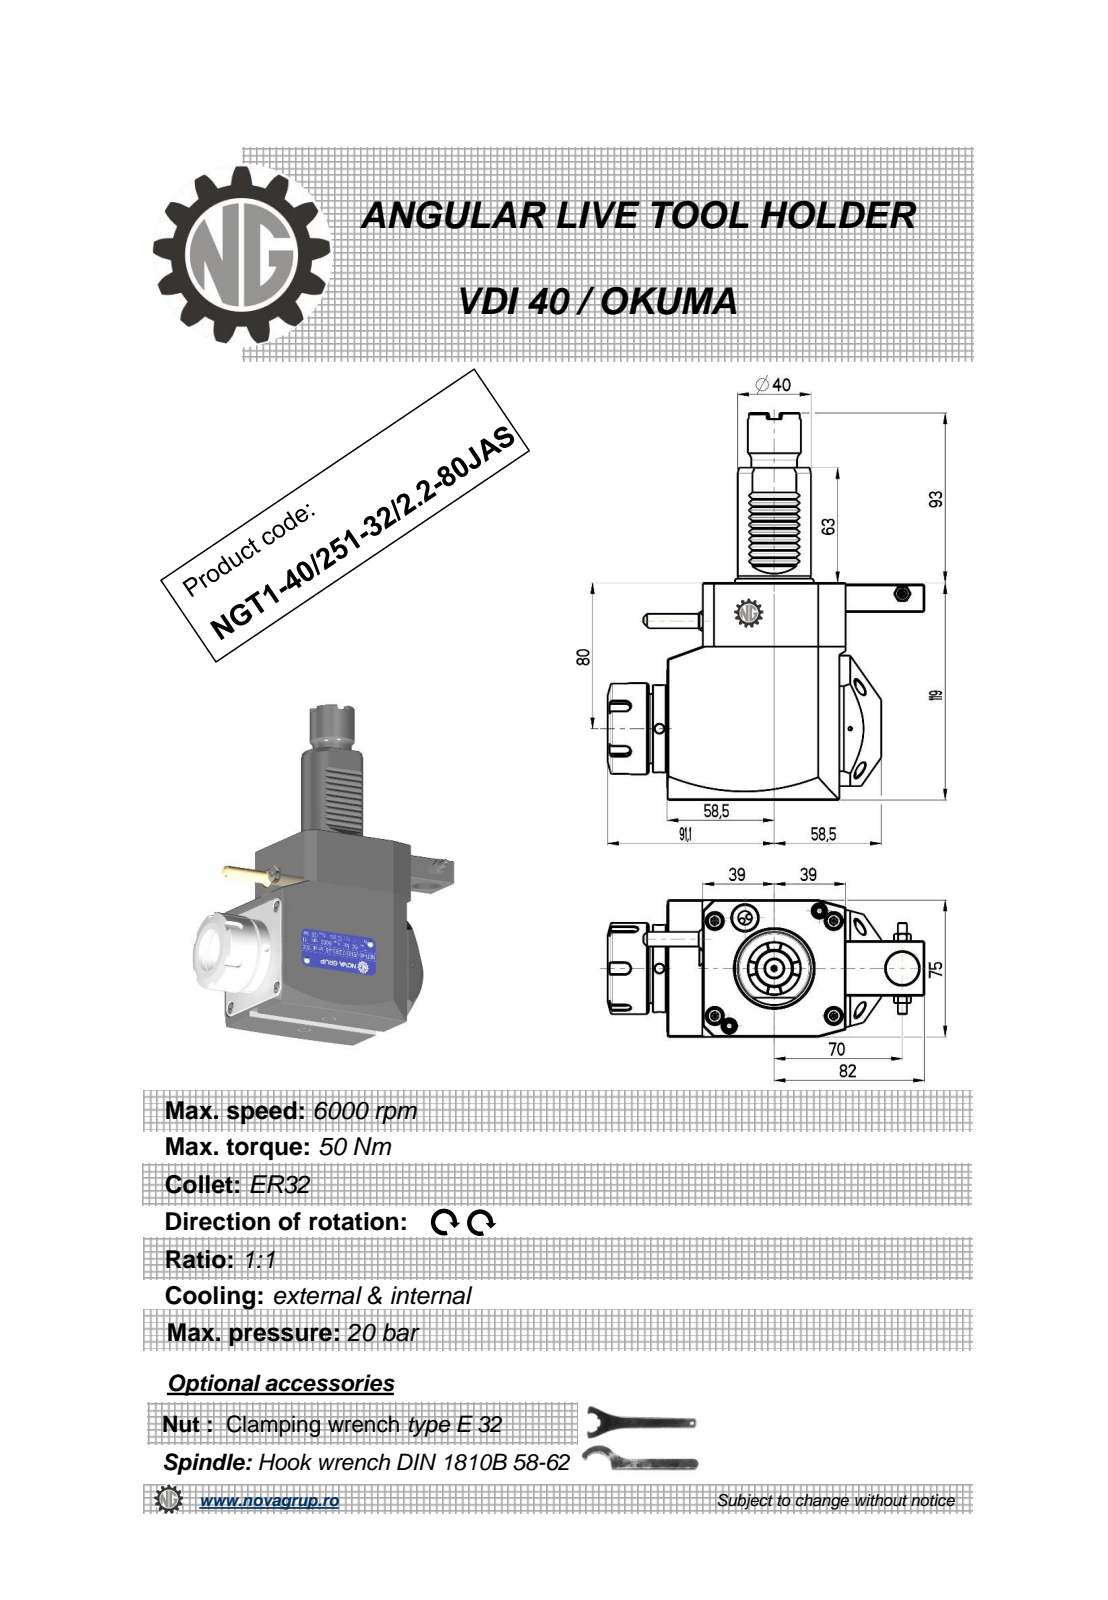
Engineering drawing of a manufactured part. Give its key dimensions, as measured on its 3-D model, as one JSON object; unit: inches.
{"part_name": "NGT1_40_251_32_2_2_80JAS", "step_written_by": "PRO/ENGINEER BY PARAMETRIC TECHNOLOGY CORPORATION, 2010280 (CONFIG_CONTROL_DESIGN)", "units": "inches", "bodies": {"solids": 1, "faces": 490, "planar": 223, "cylindrical": 100, "other": 167}, "overall_size": [8.346, 6.815, 3.016], "volume_in3": 61.76, "surface_area_in2": 124.8, "round_holes": [[0.197, 3], [0.118, 1], [0.165, 1], [0.374, 1], [0.709, 1], [1.063, 1]], "round_bosses_or_shafts": [[1.969, 1], [1.89, 1], [1.634, 1], [1.614, 1], [1.575, 1], [1.142, 1], [0.984, 1], [0.394, 1]], "partial_cylinders_radius": [[0.01, 12], [0.012, 10], [0.008, 6], [0.118, 5], [0.228, 2], [0.236, 2], [23.622, 2], [0.02, 1]], "face_to_face_distances": [2.953, 4.685, 0.768, 3.839, 3.071, 0.138, 0.039, 0.886, 3.701, 0.76], "hole_center_spacings": [0.824, 2.407, 2.854, 5.226, 5.983]}
